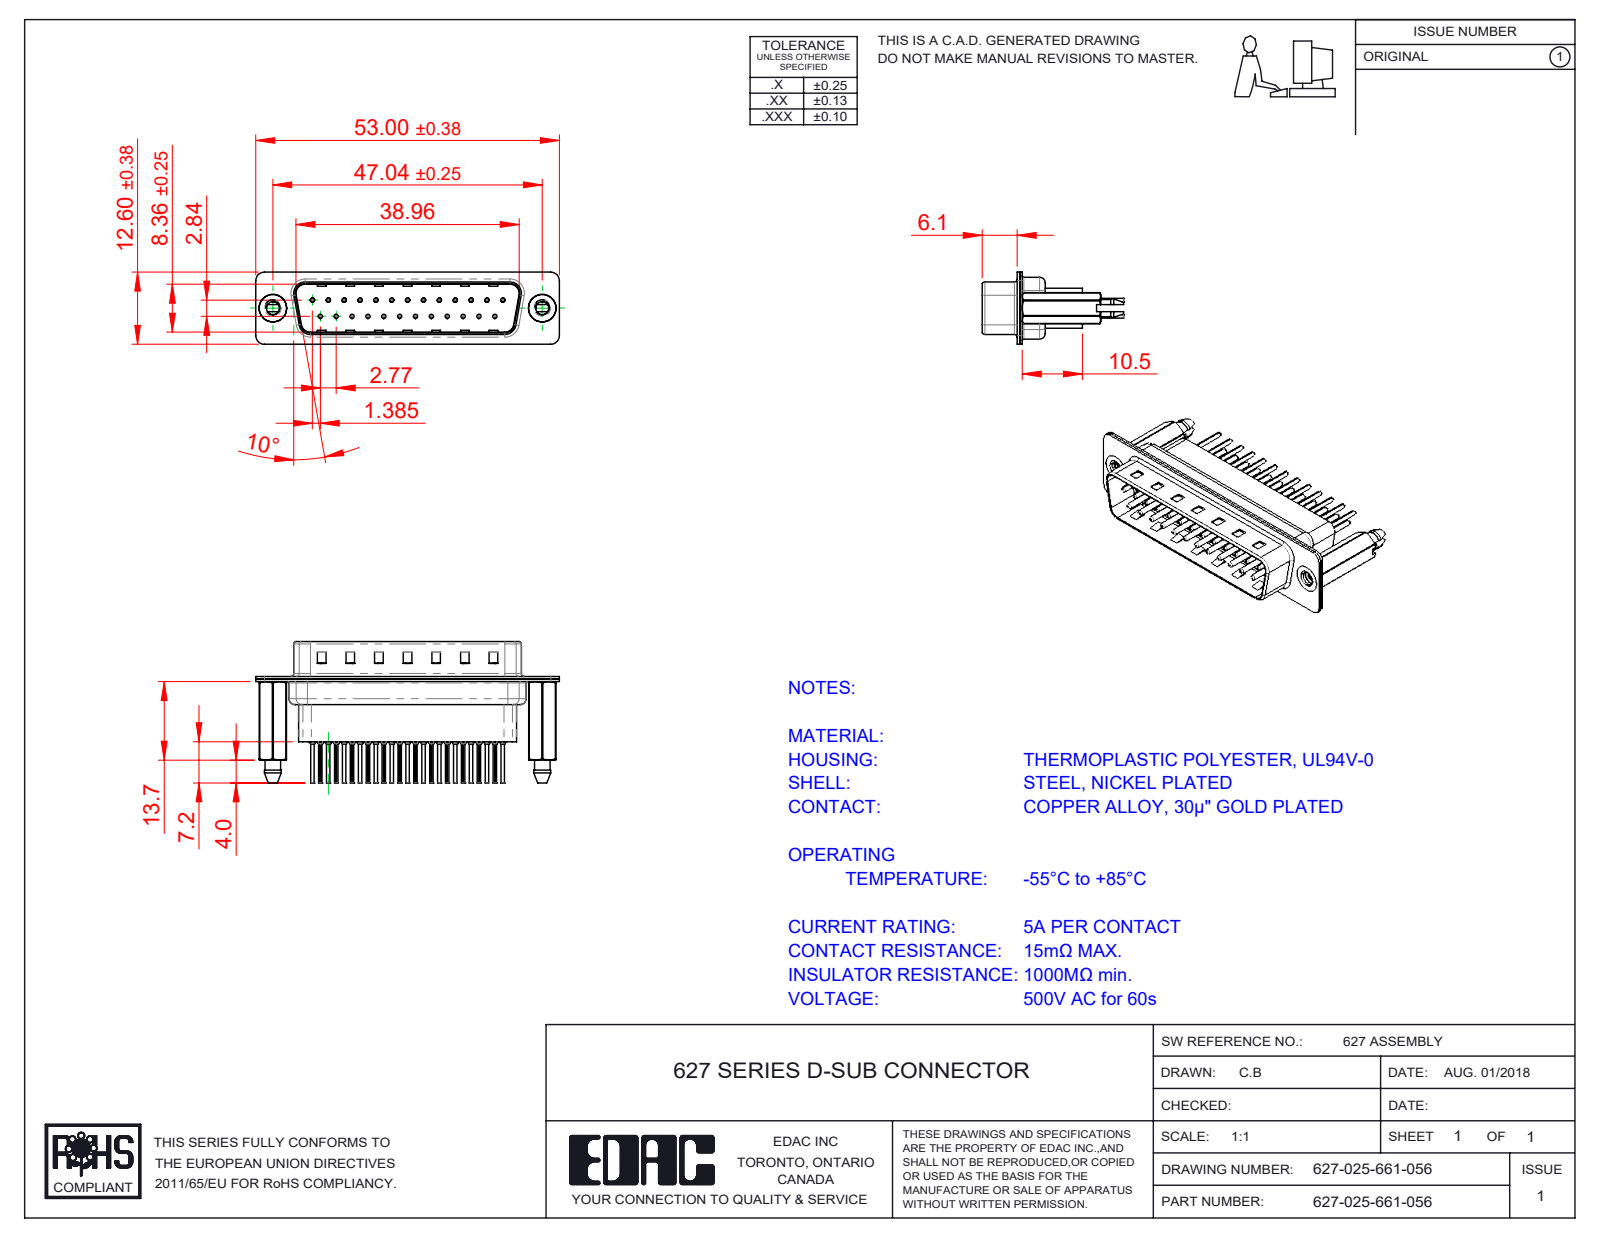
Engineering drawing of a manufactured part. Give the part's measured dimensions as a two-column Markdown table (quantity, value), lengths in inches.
| quantity | value |
| --- | --- |
| part name | 627 Shell Rear_25 Contacts; 627 Contact Row 2_61; 627 Contact Row 1_61; 627 4-40 Threaded Boardlock_HP61 (+3 more) |
| STEP written by | SolidWorks 2020 (CONFIG_CONTROL_DESIGN) |
| units | inches |
| bodies | 30 solids, 2934 faces (803 planar, 1128 cylindrical, 1003 other) |
| overall size | 2.087 × 0.969 × 0.496 |
| volume | 0.254 in³ |
| surface area | 16.69 in² |
| round holes (diameter × count) | 0.008 × 25, 0.014 × 25, 0.043 × 25, 0.063 × 25, 0.089 × 2, 0.157 × 2, 0.189 × 2 |
| round bosses / shafts (diameter × count) | 0.079 × 25, 0.059 × 25, 0.03 × 25, 0.024 × 25, 0.193 × 2 |
| partial cylindrical surfaces (radius × count) | 0.004 × 50, 0.059 × 18, 0.079 × 12, 0.063 × 10, 0.02 × 8, 0.01 × 4, 0.024 × 4, 0.026 × 4 |
| main face-to-face distances | 0.016, 0.018, 0.032, 0.377, 0.027, 0.302, 0.059, 0.035, 0.043, 0.318 |
| hole center spacings | 0.124, 0.327, 0.109, 0.218, 0.436, 0.654, 0.198, 0.198 |
